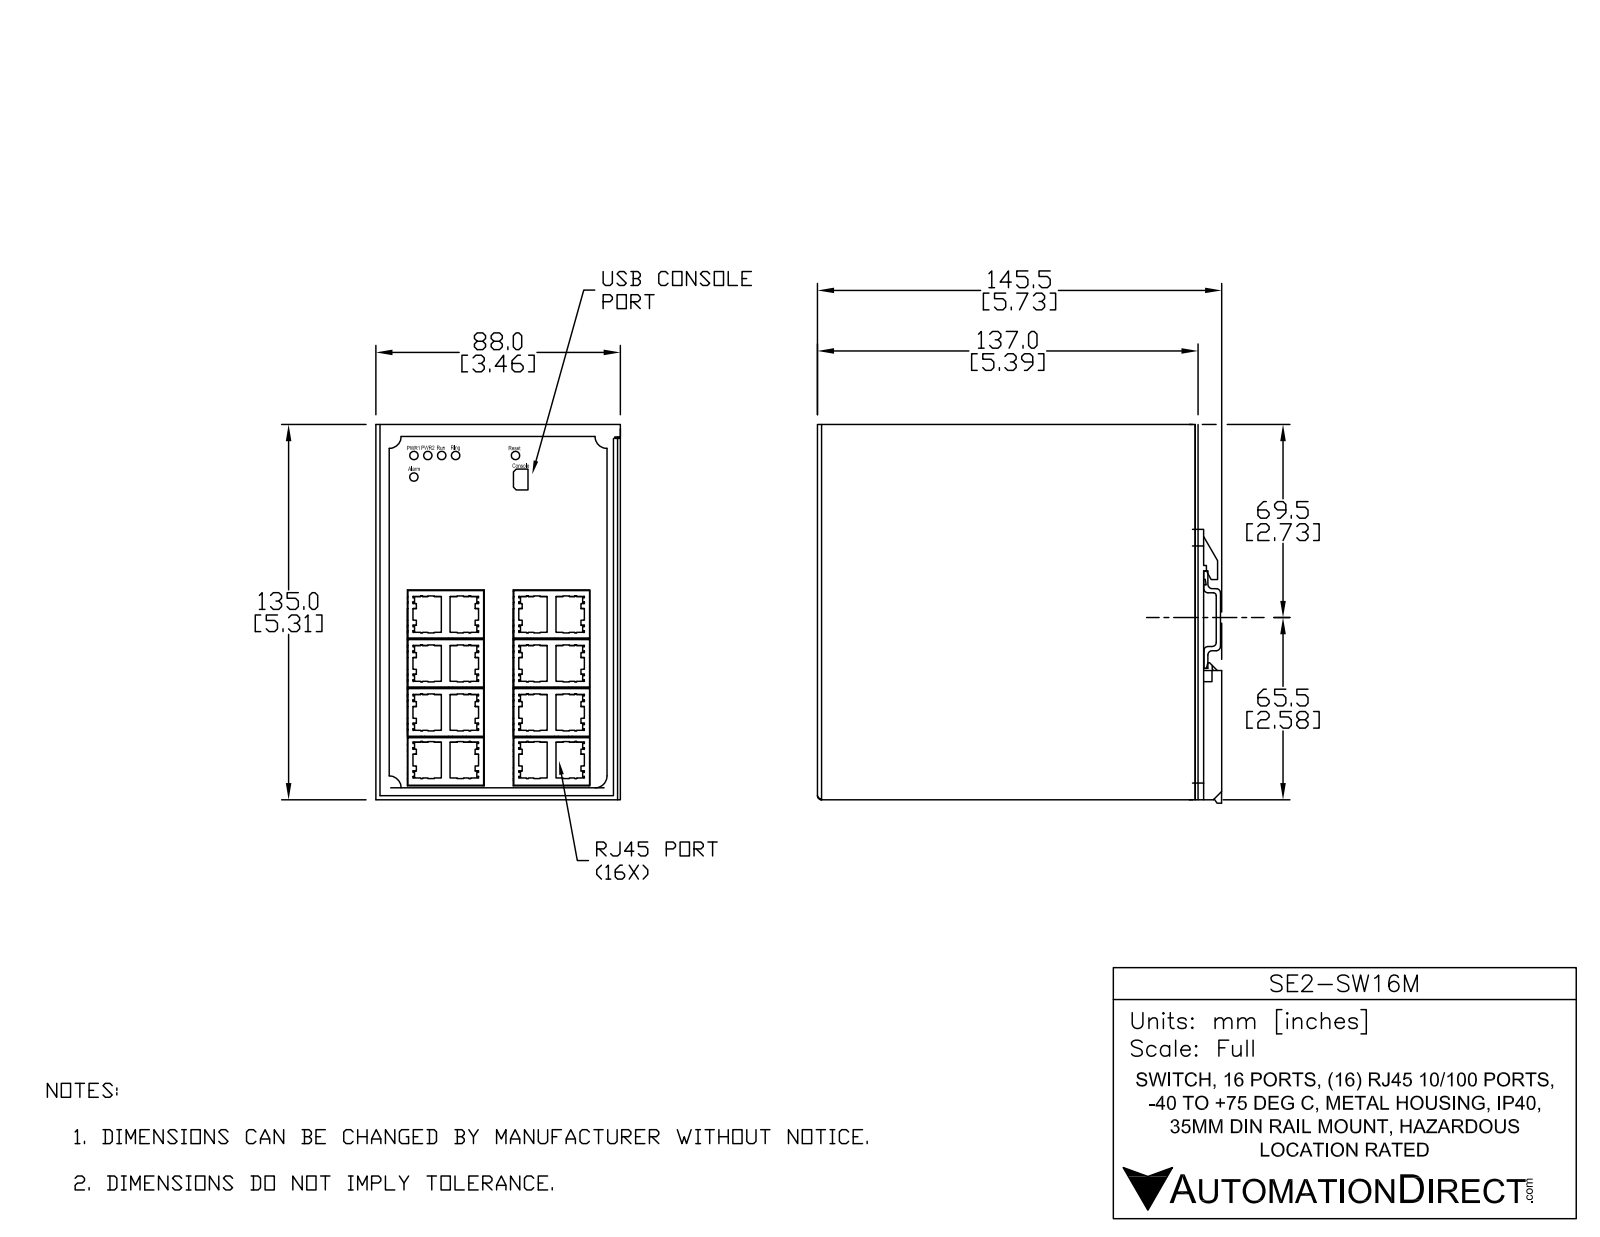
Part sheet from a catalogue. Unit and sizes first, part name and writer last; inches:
Units: inches
Overall size (bounding box): 5.827 × 5.768 × 3.48
Round holes (diameter × count): ⌀0.15 ×8, ⌀0.177 ×5, ⌀0.11 ×1
Round bosses / shafts (diameter × count): ⌀0.142 ×8, ⌀0.276 ×4, ⌀0.201 ×4, ⌀0.217 ×2, ⌀0.315 ×1, ⌀0.157 ×1
Partial cylindrical surfaces — rounded edges, fillets, slot ends (radius × count): R0.112 ×8, R0.113 ×8, R0.039 ×5, R0.012 ×4, R0.096 ×4, R0.197 ×4, R0.008 ×2, R0.079 ×2
Main face-to-face distances: 3.465, 5.315, 5.378, 5.555, 0.177, 0.016, 5.571, 0.381, 4.996, 5.174
Hole centre spacings: 0.4, 0.2, 0.2, 0.815, 1.215, 0.976, 1.015, 1.327
Volume: 99.66 in³ · Surface area: 185.3 in²
Bodies: 21 solids, 1954 faces (1597 planar, 112 cylindrical, 245 other)
Part name (STEP PRODUCT): SE2-SW16M
STEP written by: SolidWorks 2017 (AUTOMOTIVE_DESIGN)
